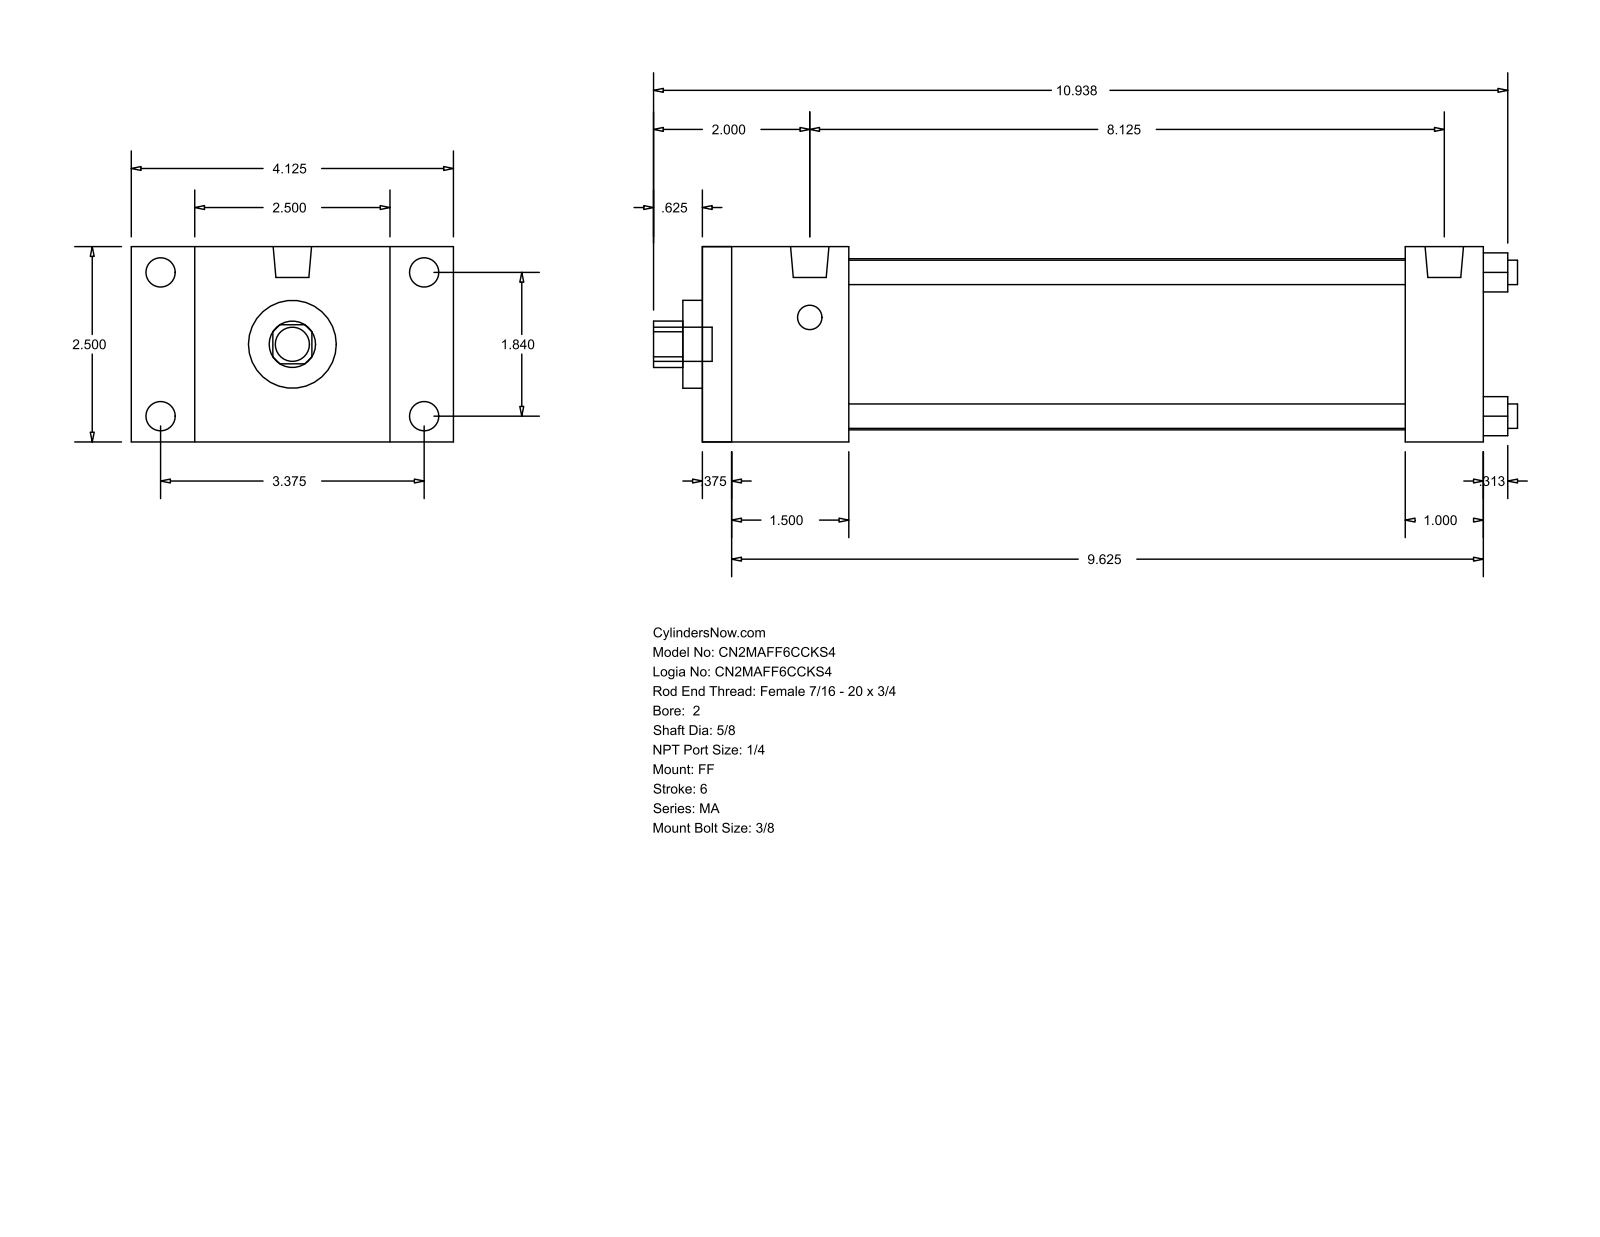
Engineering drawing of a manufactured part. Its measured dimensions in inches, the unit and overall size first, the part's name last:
Units: inches
Overall size (bounding box): 11.063 × 4.125 × 2.5
Round holes (diameter × count): ⌀0.313 ×4, ⌀0.625 ×1, ⌀1.125 ×1, ⌀2.19 ×1
Round bosses / shafts (diameter × count): ⌀0.375 ×4, ⌀0.313 ×4, ⌀0.492 ×2, ⌀0.437 ×1
Partial cylindrical surfaces — rounded edges, fillets, slot ends (radius × count): R0.297 ×1
Main face-to-face distances: 2.5, 10, 0.375, 9.625, 1.5, 1.875, 9, 8.625, 7.125, 8.125
Hole centre spacings: 1.301, 1.84, 2.602
Bodies: 0 solids, 92 faces (64 planar, 28 cylindrical, 0 other)
Part name (STEP PRODUCT): MA_FF__0200_0.625
STEP written by: GSSL Pune (CONFIG_CONTROL_DESIGN)
